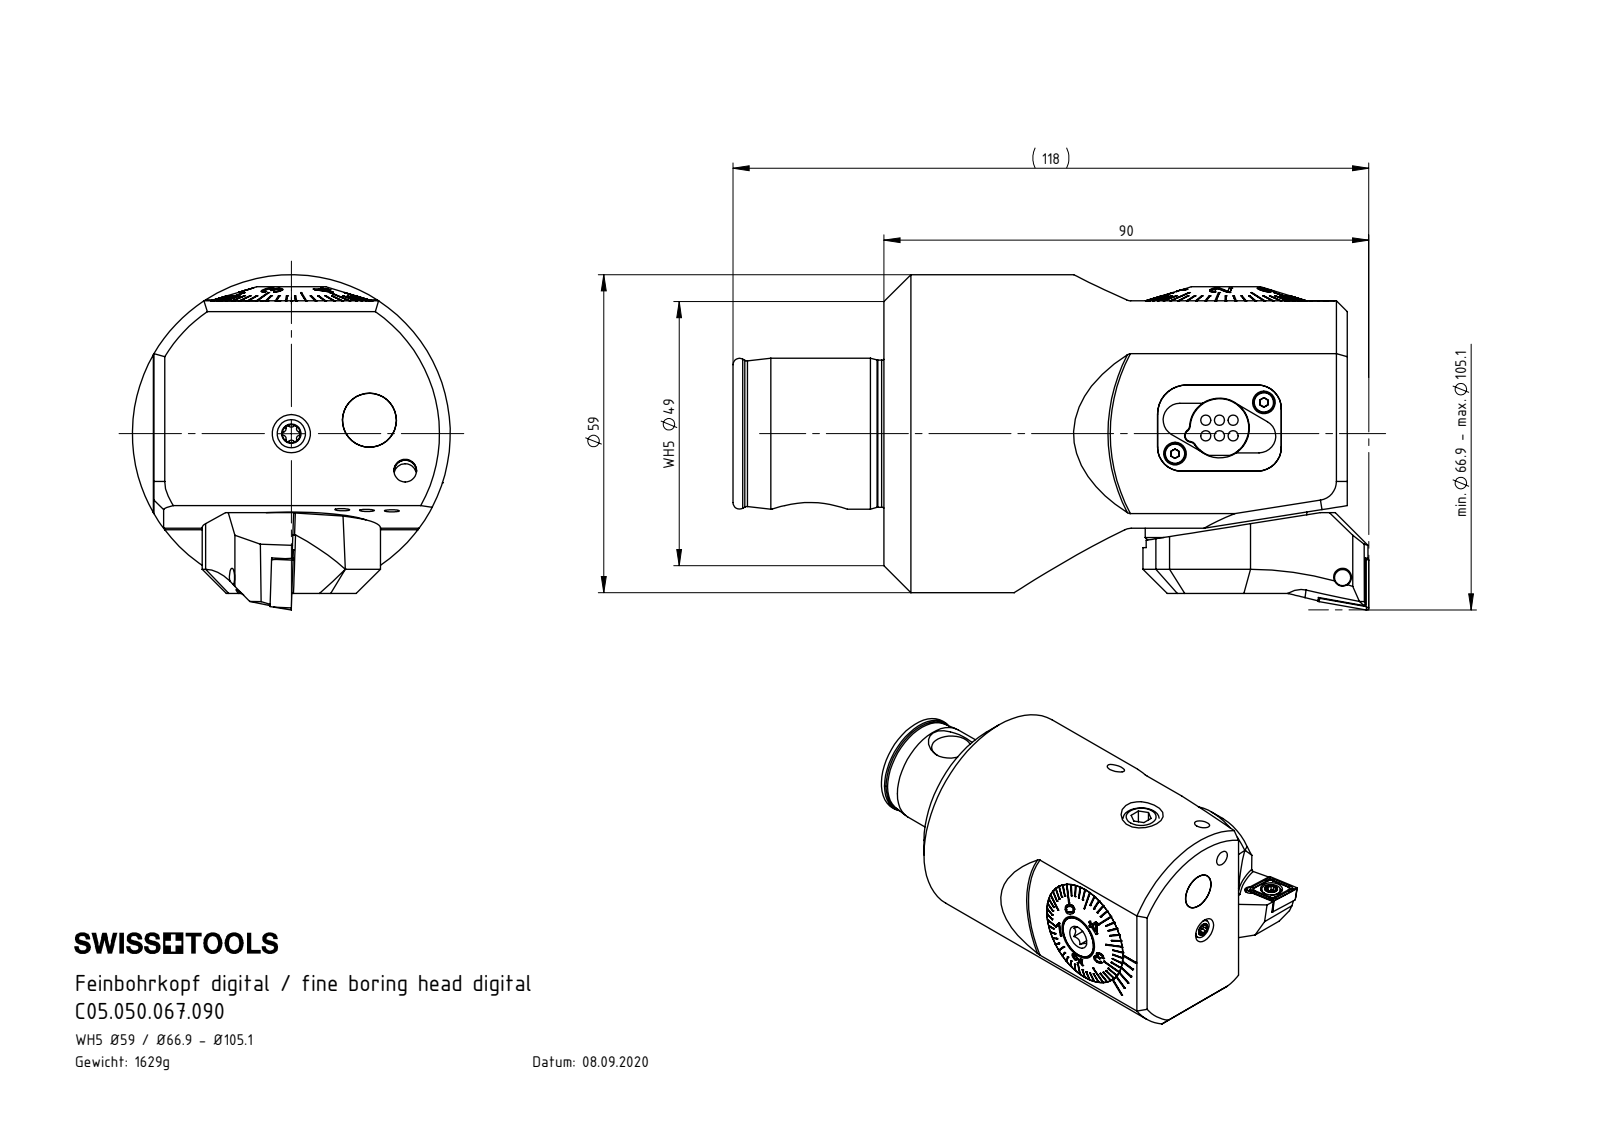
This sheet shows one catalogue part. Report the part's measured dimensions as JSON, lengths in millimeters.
{"part_name": "A55-BG2.012.006_B; DIN 3771 - 25x1.5; DIN 3771 - 13x1; F55-BG2.014.015_B (+8 more)", "step_written_by": "SolidWorks 2015 (AUTOMOTIVE_DESIGN)", "units": "millimeters", "bodies": {"solids": 29, "faces": 1213, "planar": 507, "cylindrical": 320, "other": 386}, "overall_size": [118, 65.73, 55], "volume_mm3": 201362, "surface_area_mm2": 53491, "round_holes": [[3.3, 9], [4.2, 3], [8.5, 3], [1.6, 2], [2.2, 2], [4.4, 1], [5, 1], [6.1, 1], [8, 1], [10, 1], [10.1, 1], [11, 1]], "round_bosses_or_shafts": [[1.9, 6], [10, 2], [5.25, 2], [4, 2], [3.8, 2], [2, 2], [55, 1], [50, 1]], "partial_cylinders_radius": [[0.34, 12], [0.59, 12], [1.1, 9], [1.2, 8], [0.5, 4], [4.5, 4], [3.2, 3], [4.4, 3]], "face_to_face_distances": [86, 4, 2, 2.5, 47.83, 5.3, 10, 46.65, 1.18, 36], "hole_center_spacings": [9.52, 5.72, 5.86, 9.74, 14.5, 19.04, 21, 32.5]}
